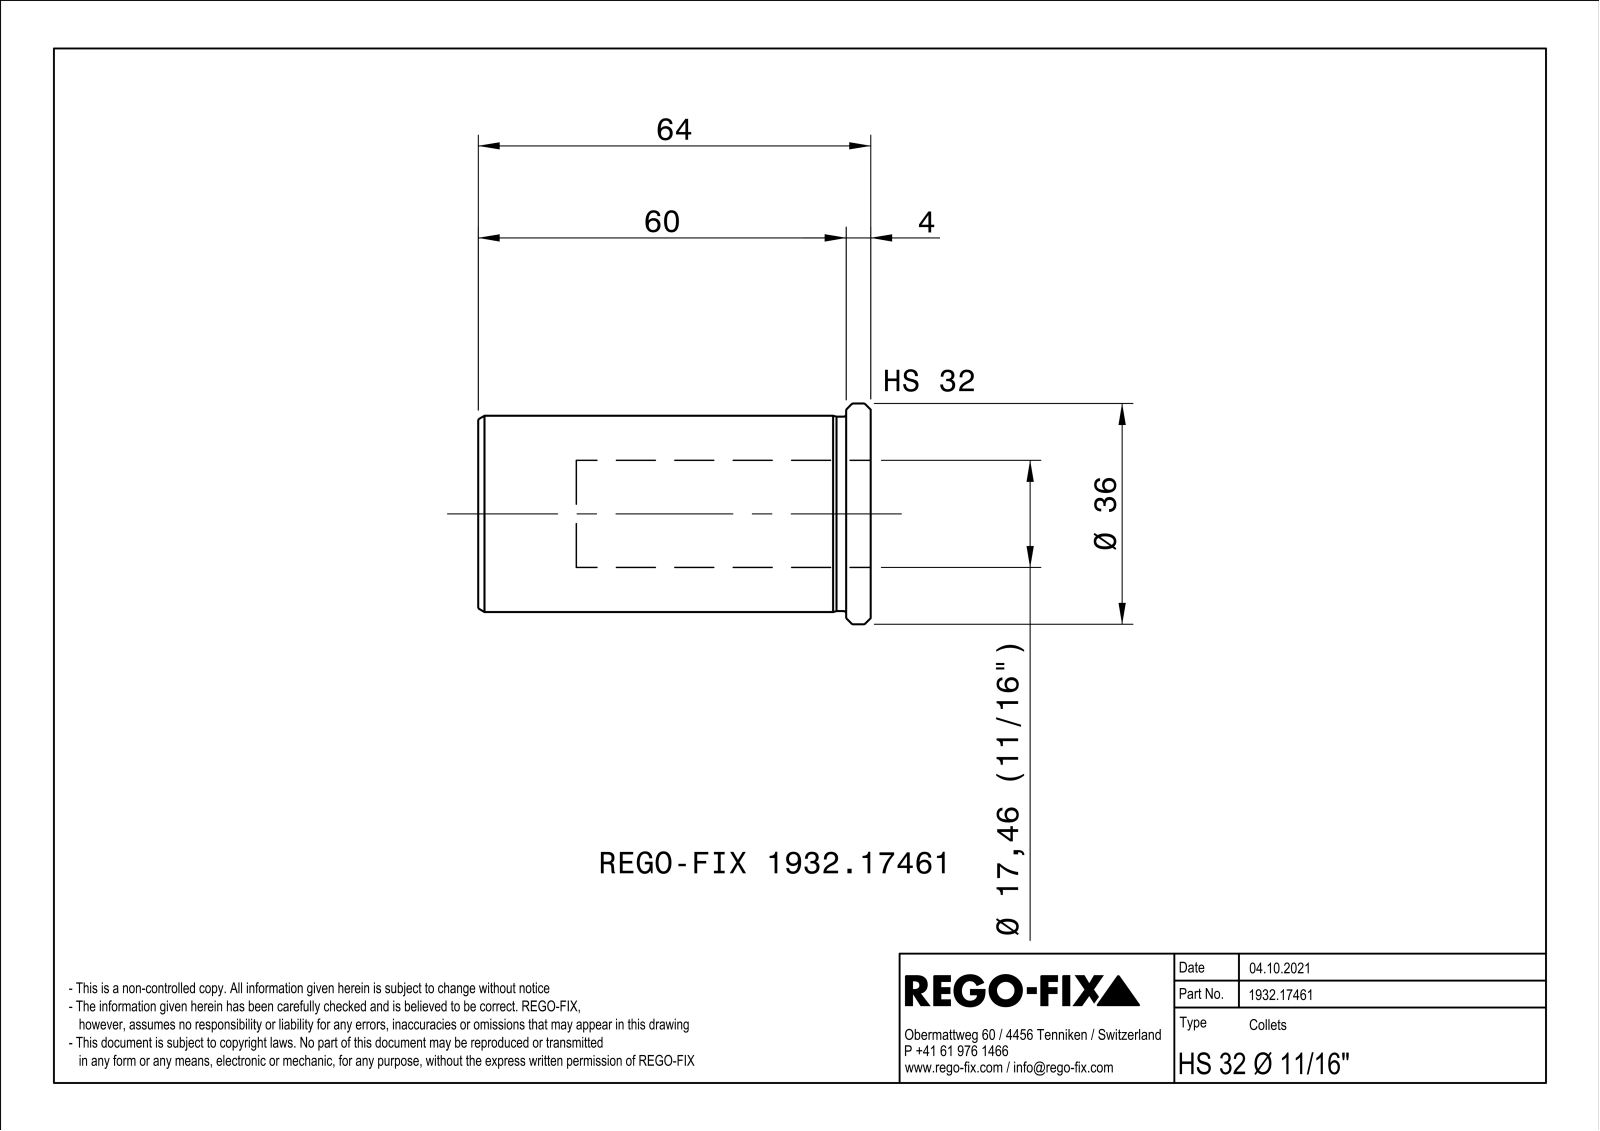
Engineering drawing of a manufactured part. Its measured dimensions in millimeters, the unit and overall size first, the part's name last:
Units: millimetres
Overall size (bounding box): 64 × 35.99 × 35.99
Round holes (diameter × count): ⌀17.46 ×1, ⌀26.5 ×1
Round bosses / shafts (diameter × count): ⌀36 ×1, ⌀32 ×1, ⌀31.7 ×1
Main face-to-face distances: 1, 64, 4, 60
Volume: 31 445 mm³ · Surface area: 13 802 mm²
Bodies: 1 solid, 70 faces (22 planar, 11 cylindrical, 37 other)
Part name (STEP PRODUCT): NOCUT
STEP written by: SIEMENS PLM Software Solid Edge ST10 (AUTOMOTIVE_DESIGN)
